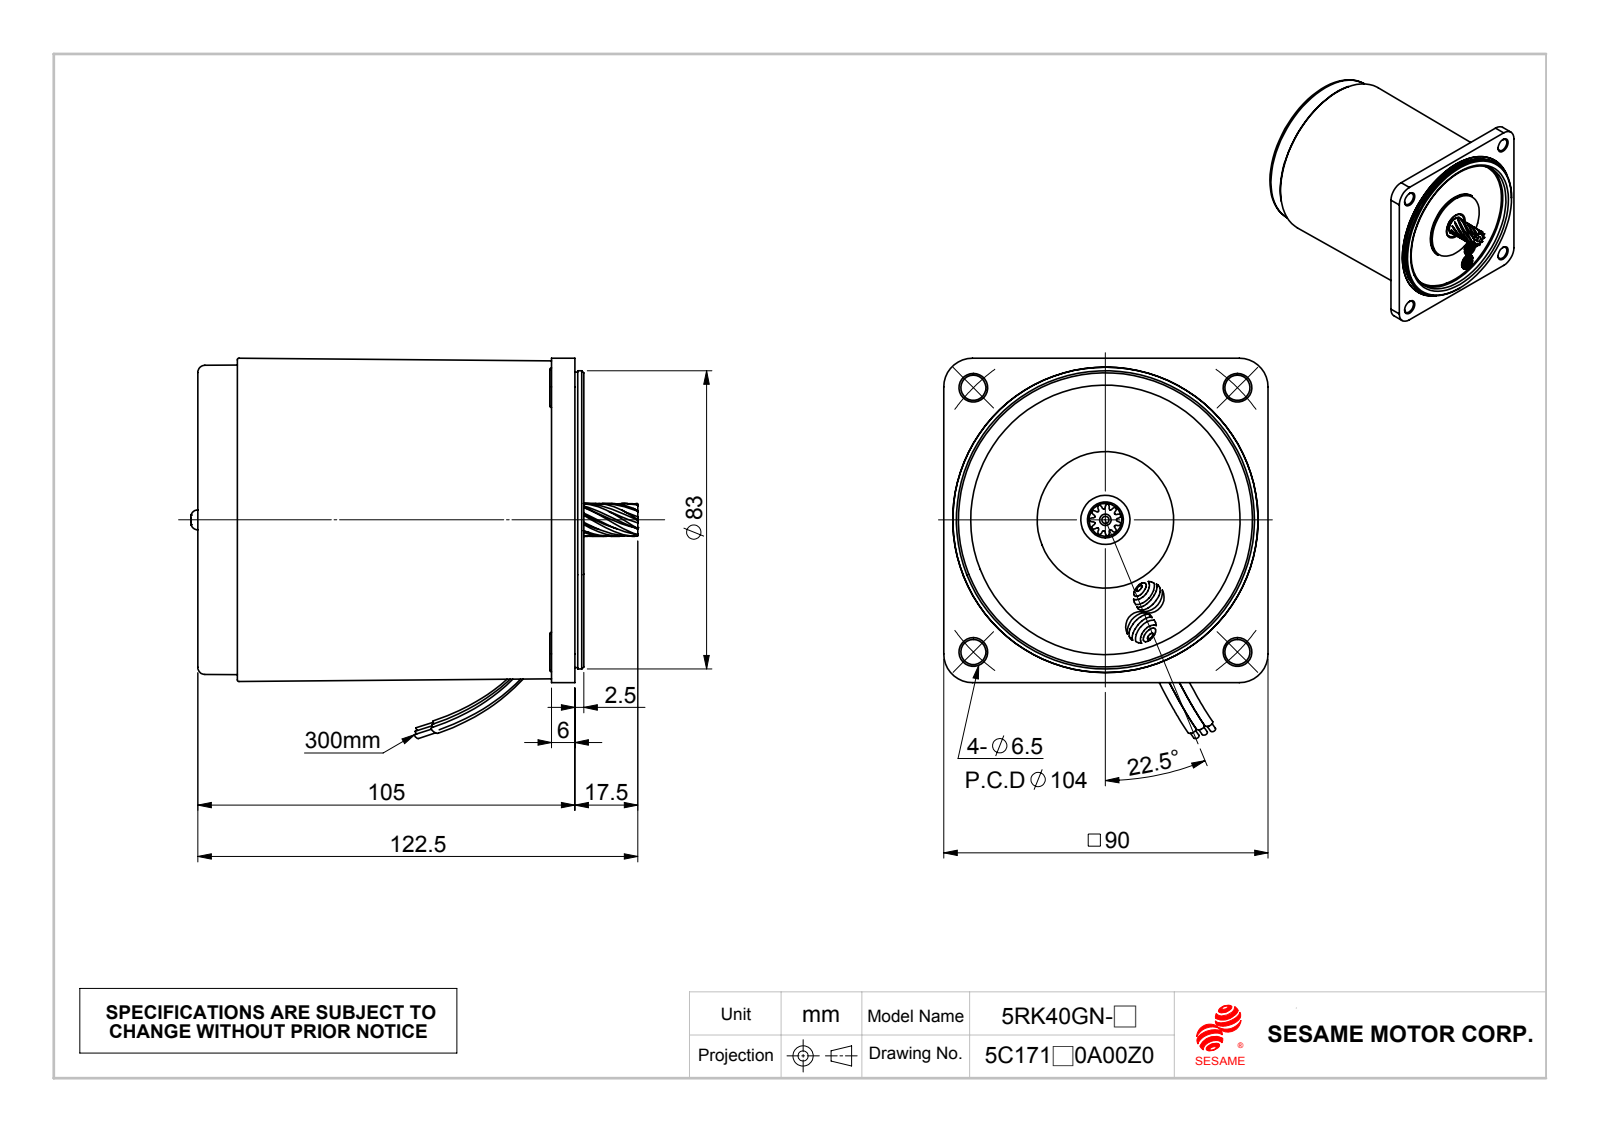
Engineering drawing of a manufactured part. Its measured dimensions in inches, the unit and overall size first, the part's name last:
Units: inches
Overall size (bounding box): 4.9 × 4.169 × 3.555
Round holes (diameter × count): ⌀0.276 ×4, ⌀0.098 ×3, ⌀0.157 ×2, ⌀0.079 ×1, ⌀0.374 ×1, ⌀0.539 ×1, ⌀1.024 ×1, ⌀2.287 ×1, ⌀2.953 ×1, ⌀3.346 ×1
Round bosses / shafts (diameter × count): ⌀0.217 ×2, ⌀0.118 ×2, ⌀3.316 ×1, ⌀3.268 ×1, ⌀3.236 ×1, ⌀1.772 ×1, ⌀1.496 ×1, ⌀0.394 ×1
Partial cylindrical surfaces — rounded edges, fillets, slot ends (radius × count): R0.012 ×8, R0.031 ×8, R0.059 ×8, R0.065 ×8, R0.115 ×8, R0.008 ×4, R0.023 ×4, R0.102 ×4
Main face-to-face distances: 0.039, 4.035, 0.035, 4.071, 3.996, 4.031, 4.075, 0.098, 4.094, 0.059
Hole centre spacings: 1.634, 2.047, 2.581, 2.895, 0.689, 4.094, 1.378
Volume: 40.59 in³ · Surface area: 102.1 in²
Bodies: 9 solids, 397 faces (77 planar, 209 cylindrical, 111 other)
Part name (STEP PRODUCT): 40GN; M540-RK; 펥짰웰찿M5즤45x1t_Default
STEP written by: SolidWorks 2010 (CONFIG_CONTROL_DESIGN)
